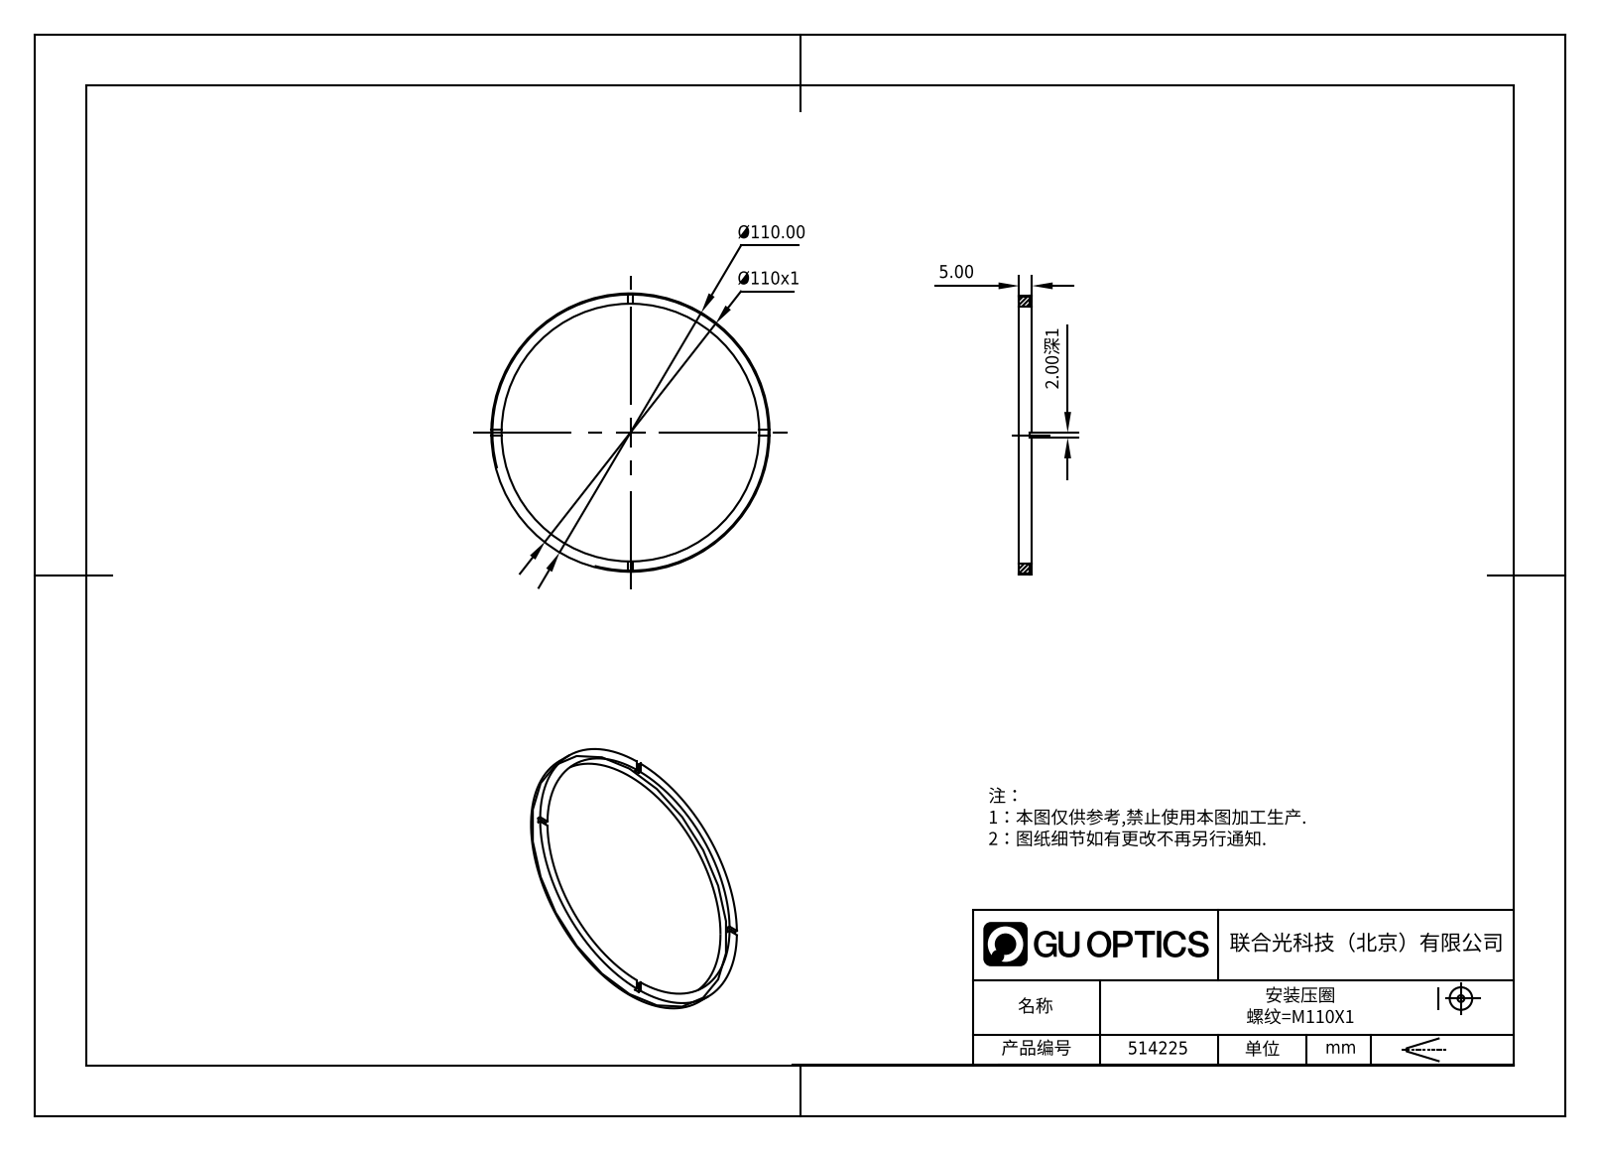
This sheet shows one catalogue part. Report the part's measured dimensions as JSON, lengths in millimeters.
{"part_name": "514225", "step_written_by": "SolidWorks 2020 (CONFIG_CONTROL_DESIGN)", "units": "millimeters", "bodies": {"solids": 1, "faces": 21, "planar": 17, "cylindrical": 4, "other": 0}, "overall_size": [110, 110, 5.5], "volume_mm3": 9031, "surface_area_mm2": 6951, "round_holes": [[100, 1]], "round_bosses_or_shafts": [[110, 1]], "face_to_face_distances": [5.5, 4.5, 1, 2]}
